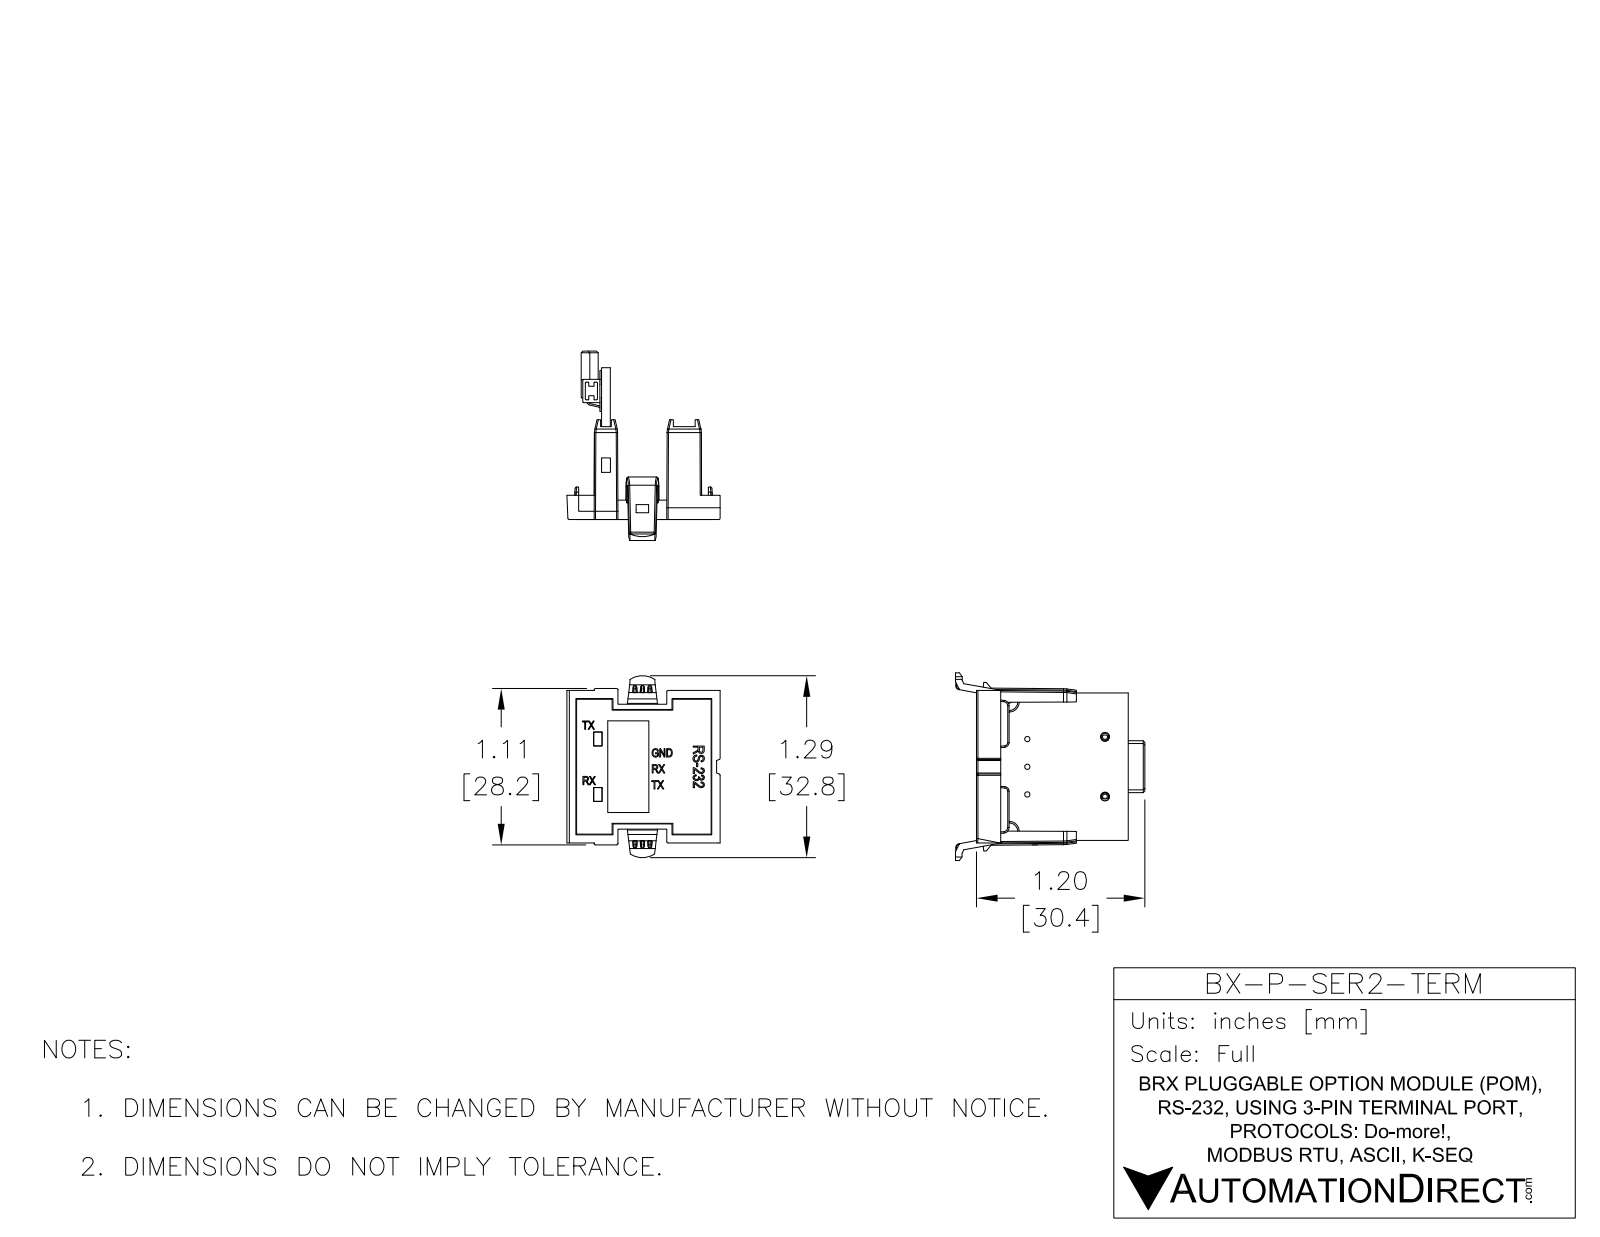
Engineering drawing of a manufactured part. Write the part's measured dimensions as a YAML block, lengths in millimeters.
part_name: "BX-P-SER2-TERM"
step_written_by: "SolidWorks 2016 (AUTOMOTIVE_DESIGN)"
units: millimeters
bodies: {solids: 54, faces: 2204, planar: 1660, cylindrical: 403, other: 141}
overall_size: [40.95, 33.88, 27.53]
volume: 5170
surface_area: 9312
round_holes:
  - {diameter: 0.25, count: 3}
  - {diameter: 0.95, count: 3}
  - {diameter: 1, count: 3}
  - {diameter: 2, count: 3}
  - {diameter: 2.8, count: 3}
  - {diameter: 1.6, count: 2}
round_bosses_or_shafts:
  - {diameter: 2.6, count: 3}
  - {diameter: 0.25, count: 3}
partial_cylinders:
  - {radius: 0.1, count: 89}
  - {radius: 0.2, count: 47}
  - {radius: 0.85, count: 10}
  - {radius: 0.14, count: 8}
  - {radius: 0.3, count: 6}
  - {radius: 0.35, count: 6}
  - {radius: 0.41, count: 5}
  - {radius: 1.25, count: 5}
face_to_face_distances: [1.58, 1.57, 0.5, 1.68, 7, 3.5, 1.67, 3, 8.44, 3.55]
hole_center_spacings: [3.5, 14.03, 14.46, 7, 14.15, 15.68, 28.11, 28.57]
